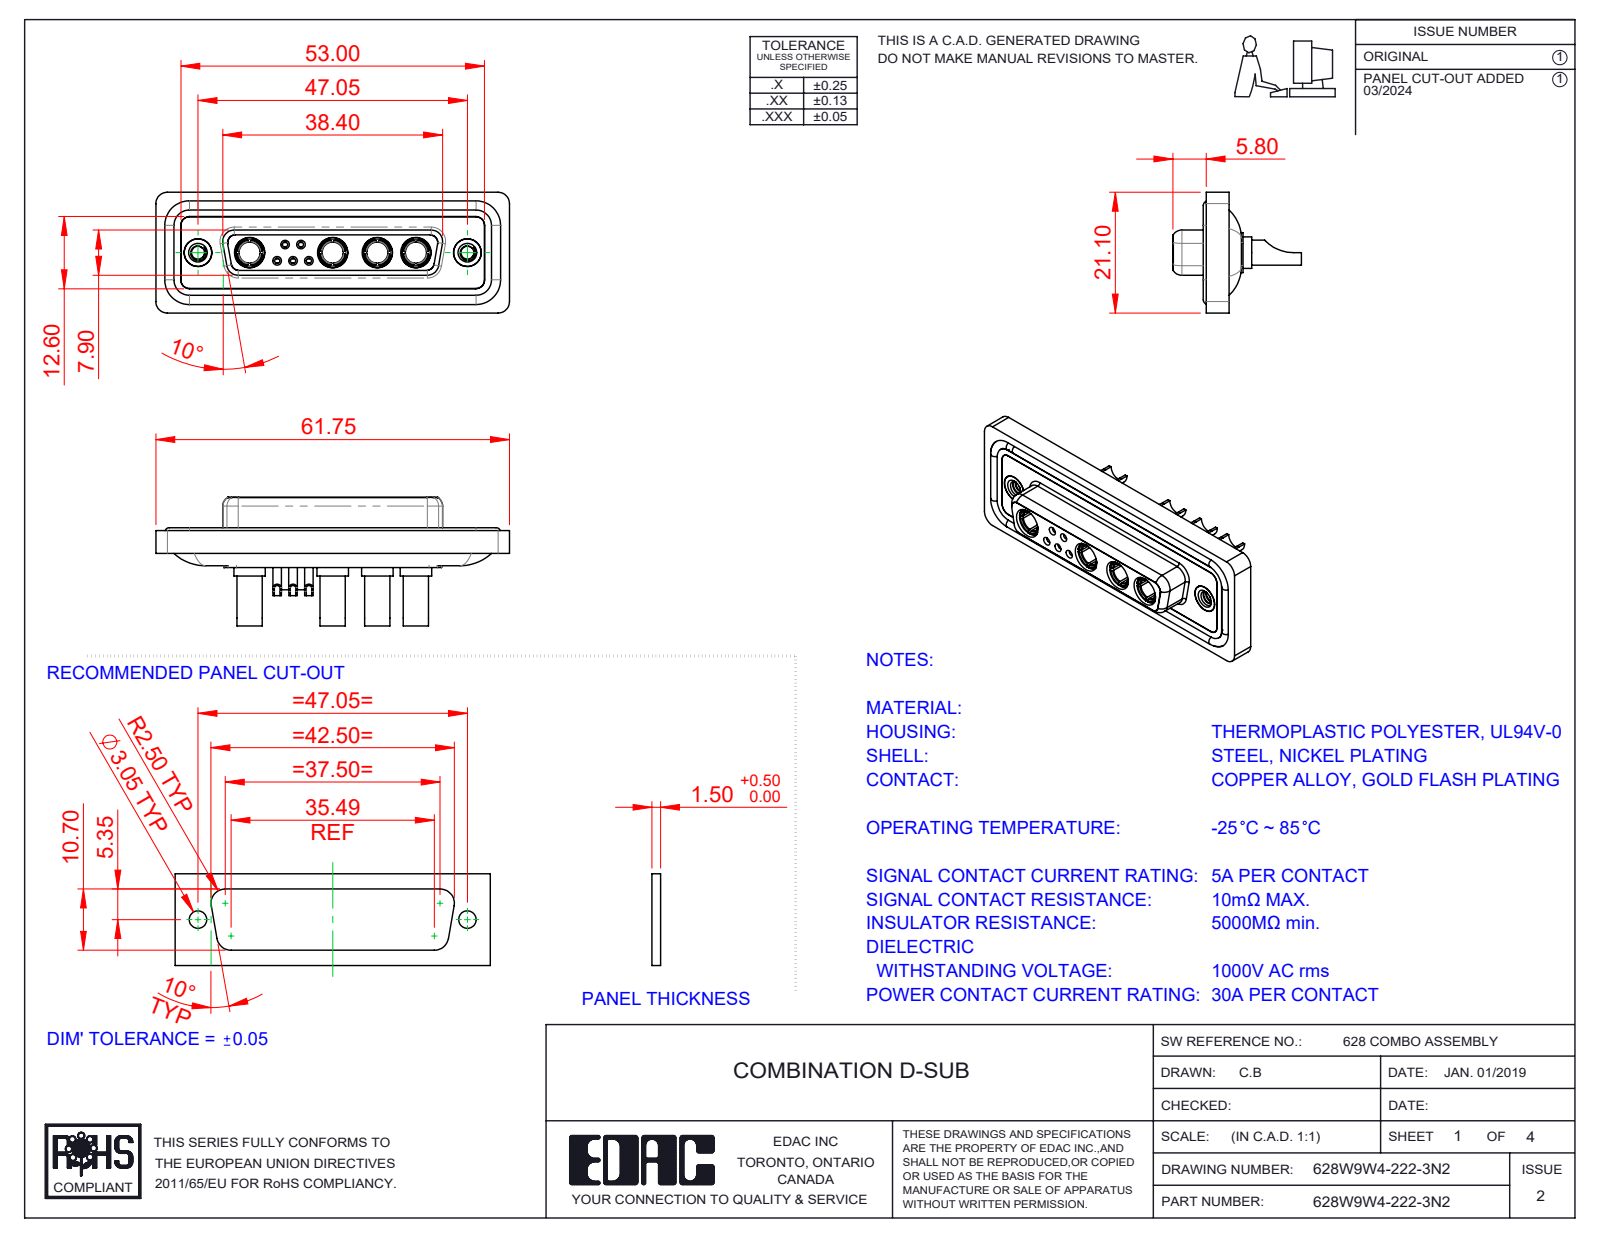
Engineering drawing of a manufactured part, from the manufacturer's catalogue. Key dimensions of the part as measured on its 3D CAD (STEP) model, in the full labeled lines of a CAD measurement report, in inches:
Part name (STEP PRODUCT): 628Combo Housing_9W4; 628Combo Shell Front_25 Contacts; 628Combo Threaded Rivet_2; 628W9W4-222-3N2 (+5 more)
STEP written by: SolidWorks 2023 (CONFIG_CONTROL_DESIGN)
Units: inches
Bodies: 20 solids, 981 faces (318 planar, 397 cylindrical, 266 other)
Overall size (bounding box): 2.431 × 0.884 × 0.831
Volume: 0.508 in³ · Surface area: 21.77 in²
Round holes (diameter × count): ⌀0.191 ×6, ⌀0.035 ×5, ⌀0.039 ×5, ⌀0.043 ×5, ⌀0.059 ×5, ⌀0.079 ×5, ⌀0.138 ×4, ⌀0.146 ×4, ⌀0.209 ×4, ⌀0.063 ×3, ⌀0.067 ×2, ⌀0.089 ×2
Round bosses / shafts (diameter × count): ⌀0.063 ×6, ⌀0.087 ×5, ⌀0.217 ×4, ⌀0.205 ×4, ⌀0.195 ×4, ⌀0.187 ×4, ⌀0.173 ×4, ⌀0.148 ×4
Partial cylindrical surfaces — rounded edges, fillets, slot ends (radius × count): R0.059 ×22, R0.079 ×18, R0.053 ×8, R0.063 ×8, R0.039 ×6, R0.01 ×4, R0.02 ×4, R0.024 ×4
Main face-to-face distances: 0.016, 0.071, 0.293, 0.222, 0.02, 0.278, 0.26, 0.063, 0.043, 0.114
Hole centre spacings: 0.124, 0.109, 0.198, 0.109, 0.173, 0.198, 0.218, 0.226
